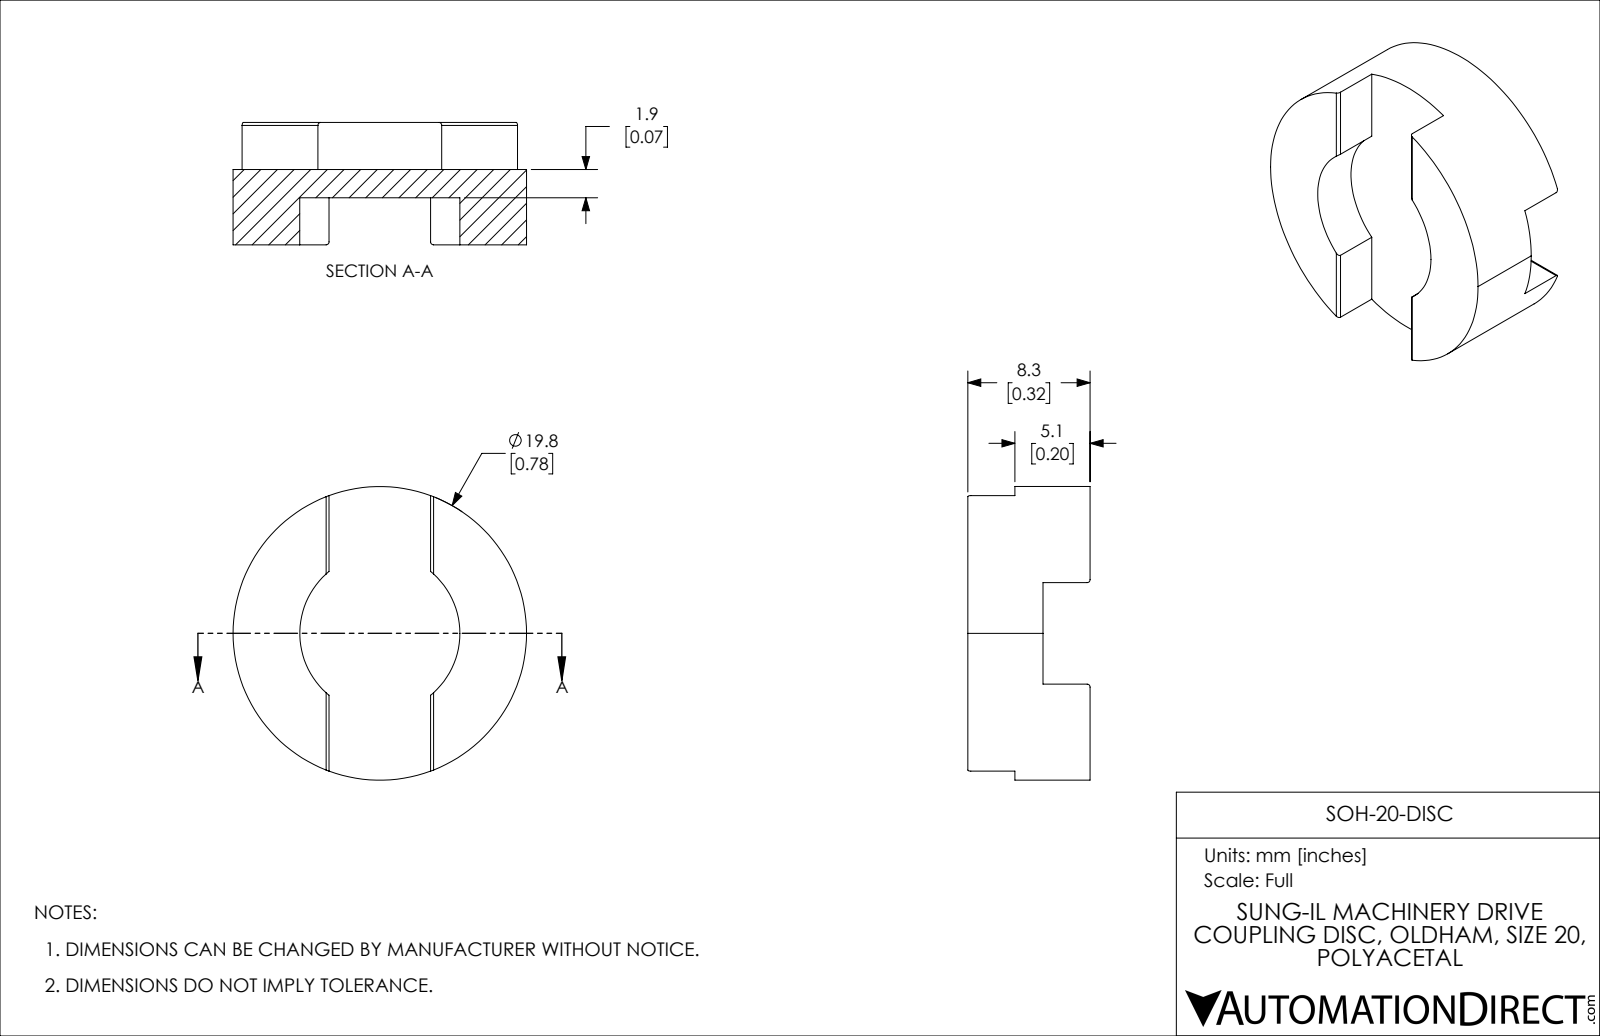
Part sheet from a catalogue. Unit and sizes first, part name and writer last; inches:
Units: inches
Overall size (bounding box): 0.78 × 0.78 × 0.325
Round holes (diameter × count): ⌀0.425 ×1
Round bosses / shafts (diameter × count): ⌀0.78 ×1
Partial cylindrical surfaces — rounded edges, fillets, slot ends (radius × count): R0.008 ×4
Main face-to-face distances: 0.125, 0.2, 0.075, 0.324, 0.27
Volume: 0.095 in³ · Surface area: 1.996 in²
Bodies: 1 solid, 29 faces (14 planar, 15 cylindrical, 0 other)
Part name (STEP PRODUCT): SOH-20-DISC
STEP written by: SolidWorks 2021 (CONFIG_CONTROL_DESIGN)
